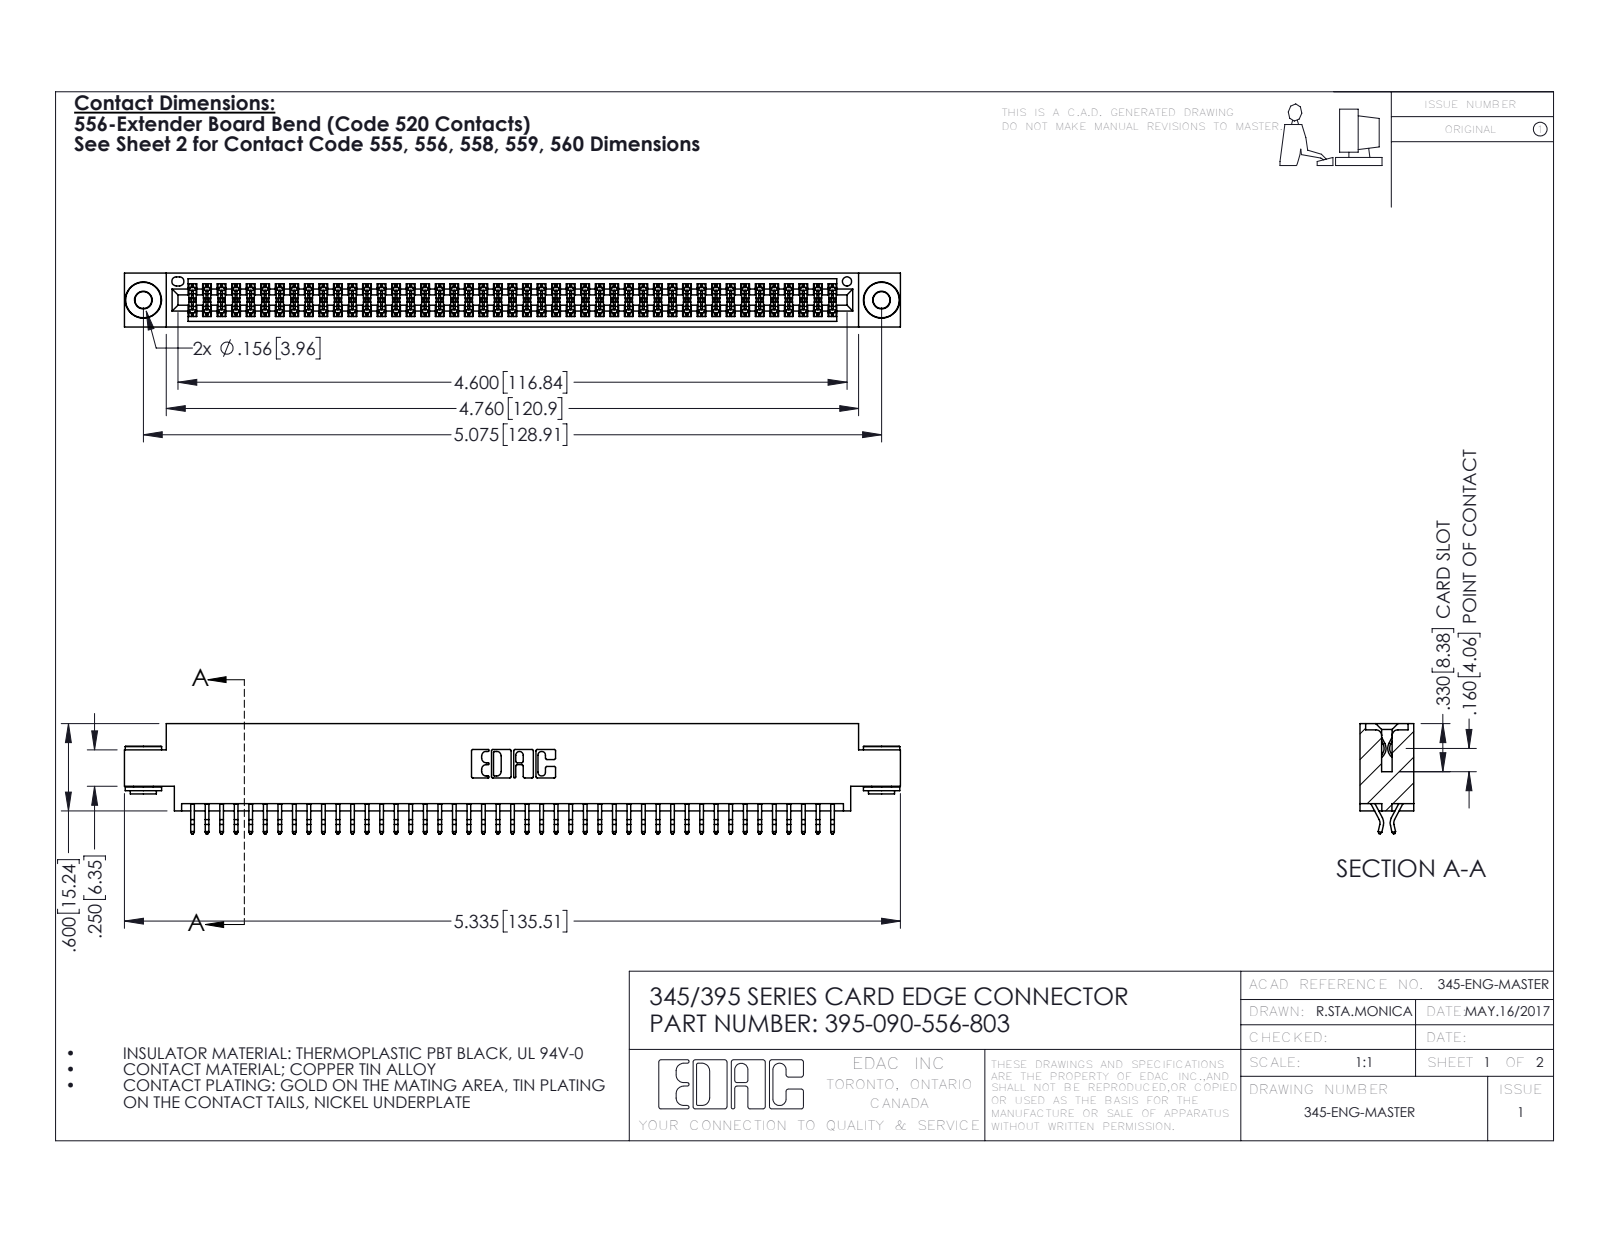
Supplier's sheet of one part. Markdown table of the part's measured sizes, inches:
| quantity | value |
| --- | --- |
| part name | 345 Part_0.170 Offset - 0.156 Dia-TH; 345-250-002_345-250-002-102; 395-090-556-803; 345-292-001_556 Tail |
| STEP written by | SolidWorks 2016 (CONFIG_CONTROL_DESIGN) |
| units | inches |
| bodies | 93 solids, 5208 faces (3424 planar, 1776 cylindrical, 8 other) |
| overall size | 5.335 × 0.757 × 0.37 |
| volume | 0.799 in³ |
| surface area | 30.51 in² |
| round holes (diameter × count) | 0.116 × 2, 0.156 × 2, 0.064 × 1 |
| round bosses / shafts (diameter × count) | 0.25 × 2, 0.18 × 2, 0.136 × 2 |
| partial cylindrical surfaces (radius × count) | 0.006 × 135, 0.01 × 22, 0.007 × 6, 0.031 × 6, 0.026 × 3, 0.01 × 2, 0.014 × 2, 0.019 × 2 |
| main face-to-face distances | 0.072, 0.298, 0.37, 0.2, 0.025, 0.098, 0.272, 0.225, 0.175, 0.149 |
| hole center spacings | 0.27, 4.839, 5.075 |
